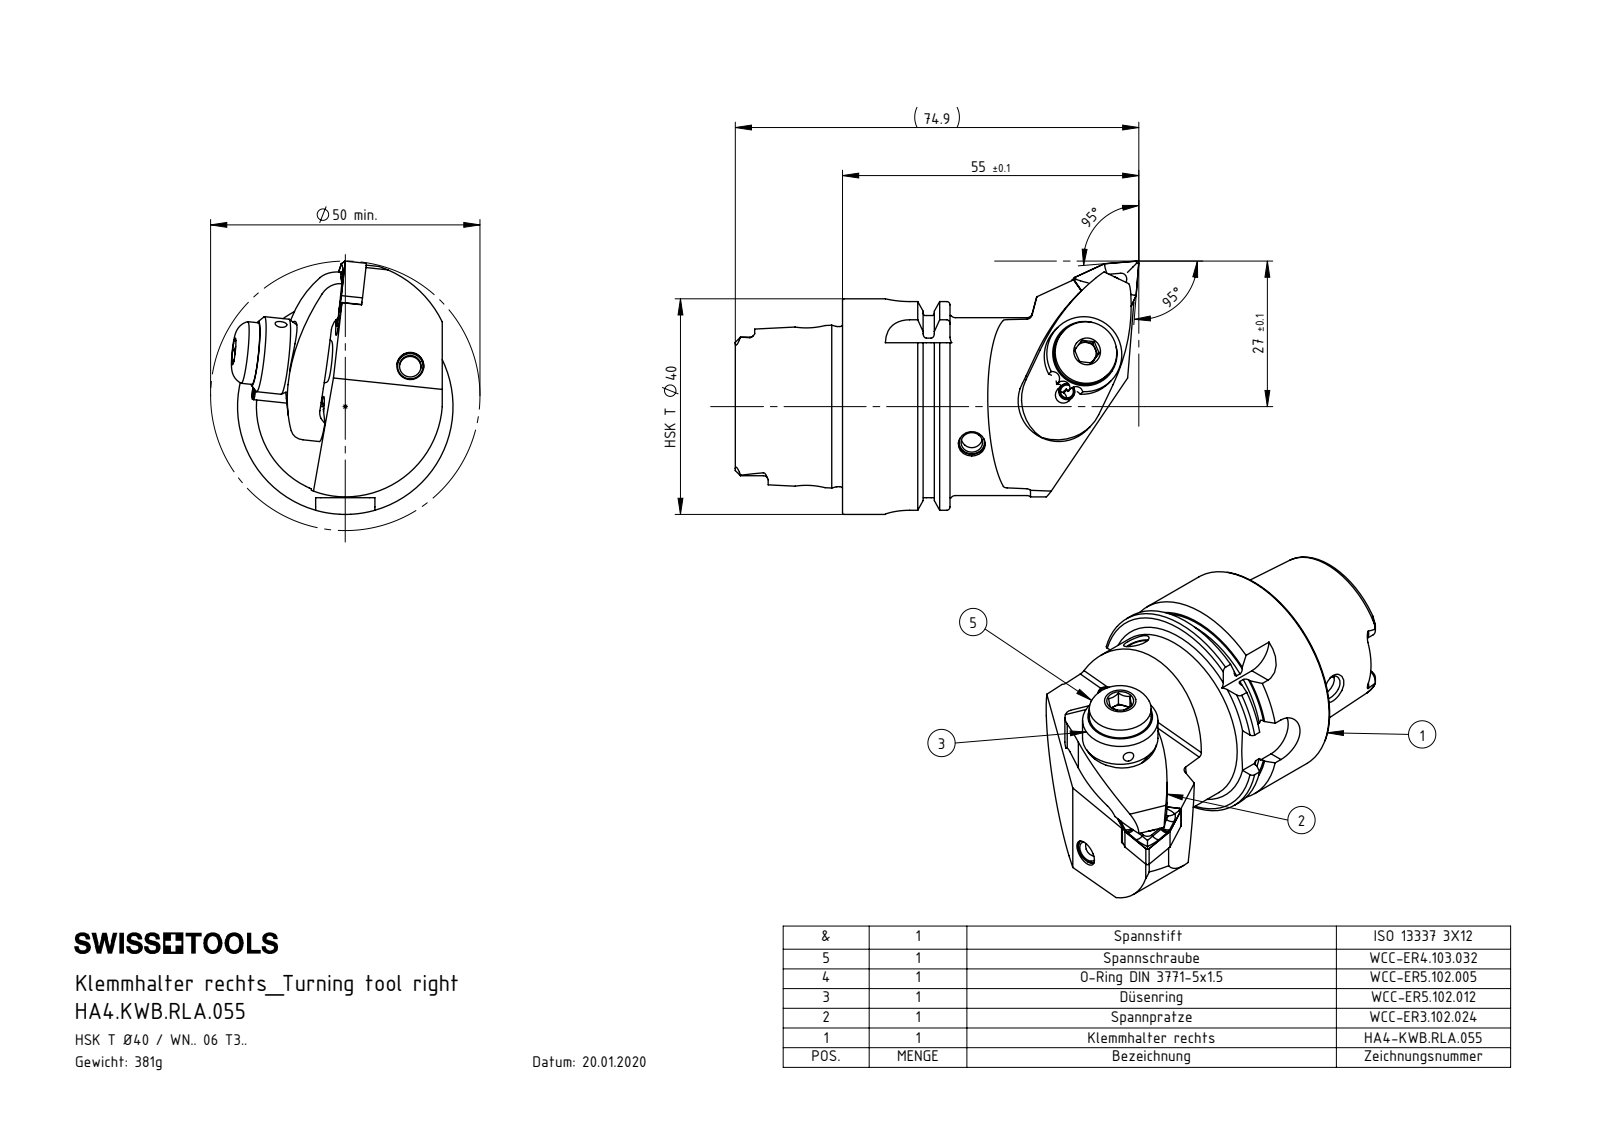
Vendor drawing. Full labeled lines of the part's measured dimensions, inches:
Part name (STEP PRODUCT): WCC-ER5.102.012_B; WCC-ER4.103.032_A; WNMG06T304; HA4-KWB.RLA.055_A_Fertigbearbeitung (+5 more)
STEP written by: SolidWorks 2017 (AUTOMOTIVE_DESIGN)
Units: inches
Bodies: 11 solids, 336 faces (121 planar, 90 cylindrical, 125 other)
Overall size (bounding box): 2.949 × 1.85 × 1.619
Volume: 2.948 in³ · Surface area: 28.53 in²
Round holes (diameter × count): ⌀0.197 ×4, ⌀0.079 ×3, ⌀0.157 ×2, ⌀0.165 ×2, ⌀0.276 ×2, ⌀0.094 ×1, ⌀0.118 ×1, ⌀0.181 ×1, ⌀0.183 ×1, ⌀0.244 ×1, ⌀0.335 ×1, ⌀0.394 ×1
Round bosses / shafts (diameter × count): ⌀0.197 ×2, ⌀0.118 ×2, ⌀1.575 ×1, ⌀1.368 ×1, ⌀1.299 ×1, ⌀1.17 ×1, ⌀0.551 ×1, ⌀0.453 ×1
Partial cylindrical surfaces — rounded edges, fillets, slot ends (radius × count): R0.035 ×6, R0.177 ×4, R0.016 ×3, R0.059 ×3, R0.079 ×3, R0.072 ×2, R0.074 ×2, R0.118 ×2
Main face-to-face distances: 0.313, 0.051, 0.472, 0.785, 0.144, 0.196, 0.783, 1.096, 1.569, 1.406
Hole centre spacings: 0.305, 0.896, 0.018, 0.018, 0.304, 0.305, 0.322, 0.323
